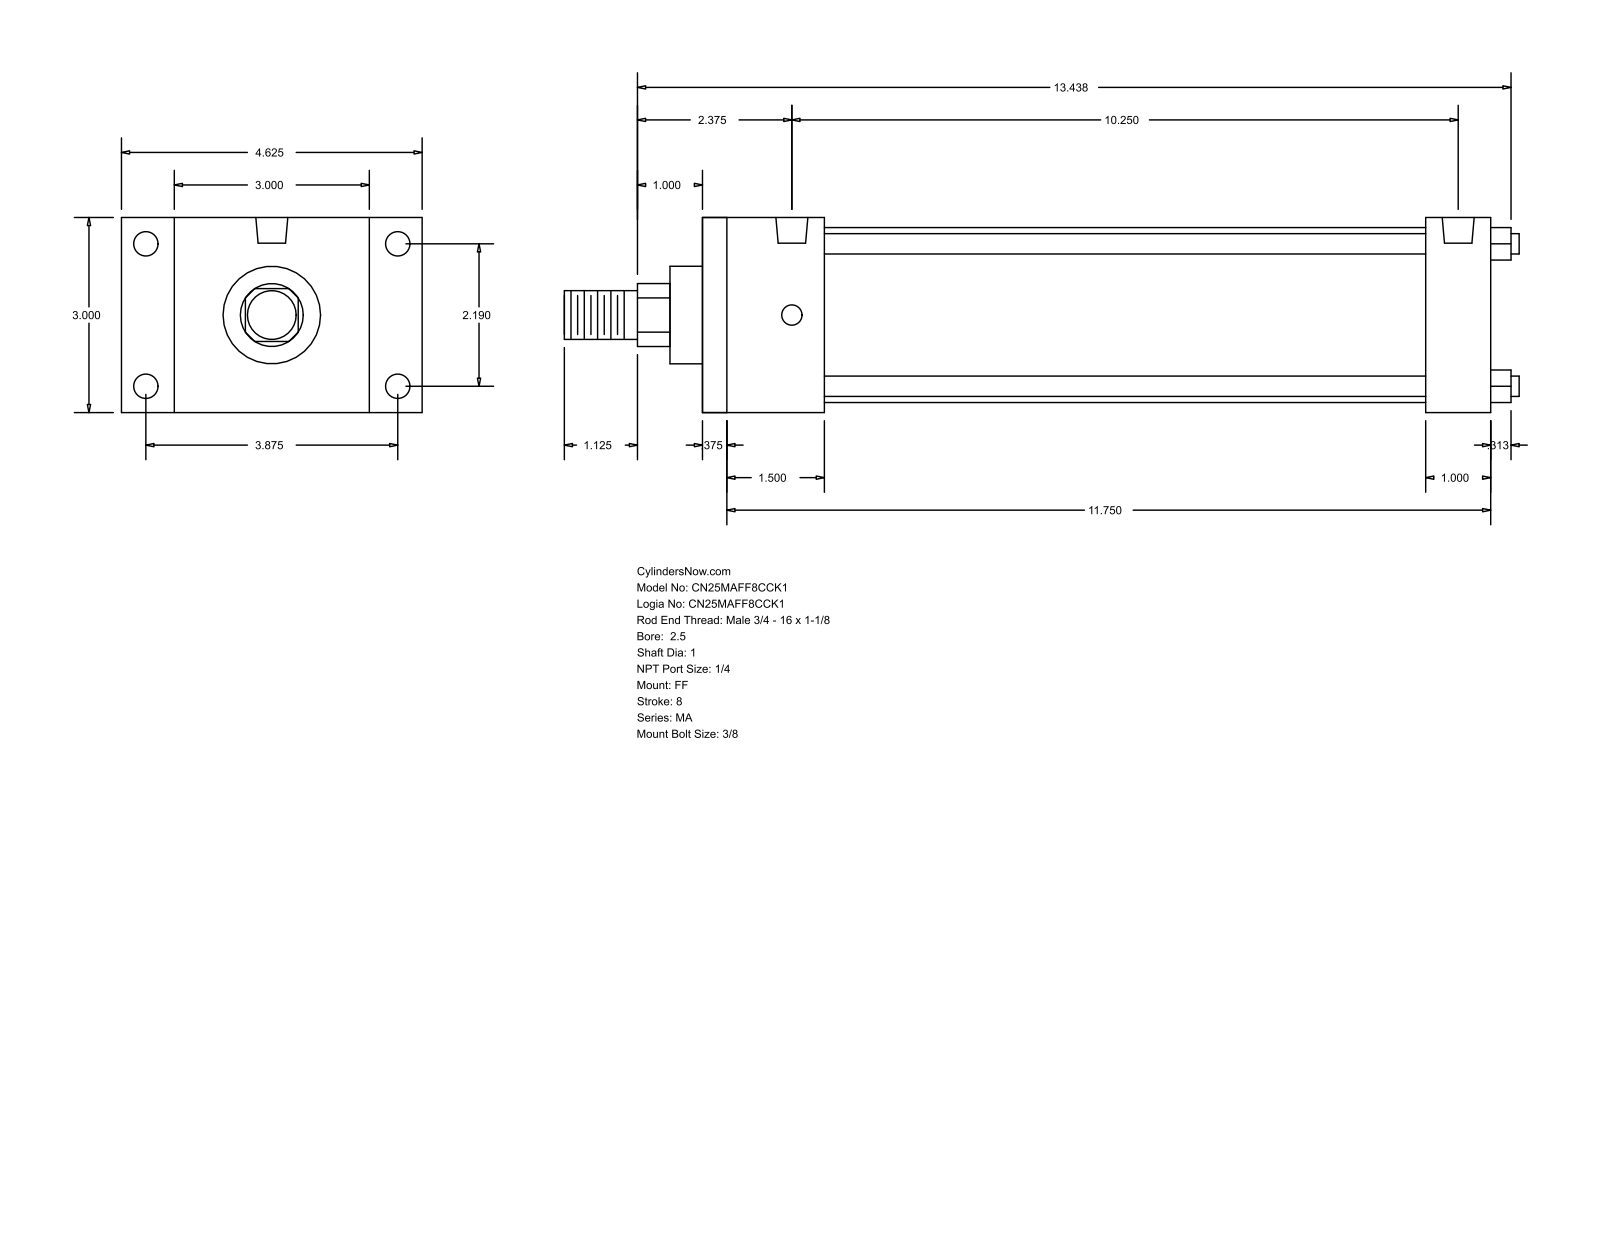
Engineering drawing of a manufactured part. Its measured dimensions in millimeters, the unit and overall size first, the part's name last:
Units: millimetres
Overall size (bounding box): 373.06 × 117.47 × 76.2
Round holes (diameter × count): ⌀7.94 ×4, ⌀9.53 ×4, ⌀12.49 ×2
Round bosses / shafts (diameter × count): ⌀7.94 ×4, ⌀68.33 ×1, ⌀38.1 ×1, ⌀25.4 ×1, ⌀19.05 ×1
Partial cylindrical surfaces — rounded edges, fillets, slot ends (radius × count): R12.29 ×1
Main face-to-face distances: 76.2, 307.98, 9.52, 298.46, 25.4, 47.63, 282.58, 38.11, 273.06, 234.95
Hole centre spacings: 55.62, 98.42, 113.05, 260.35
Bodies: 0 solids, 92 faces (64 planar, 28 cylindrical, 0 other)
Part name (STEP PRODUCT): MA_FF__0250_1
STEP written by: GSSL Pune (CONFIG_CONTROL_DESIGN)
